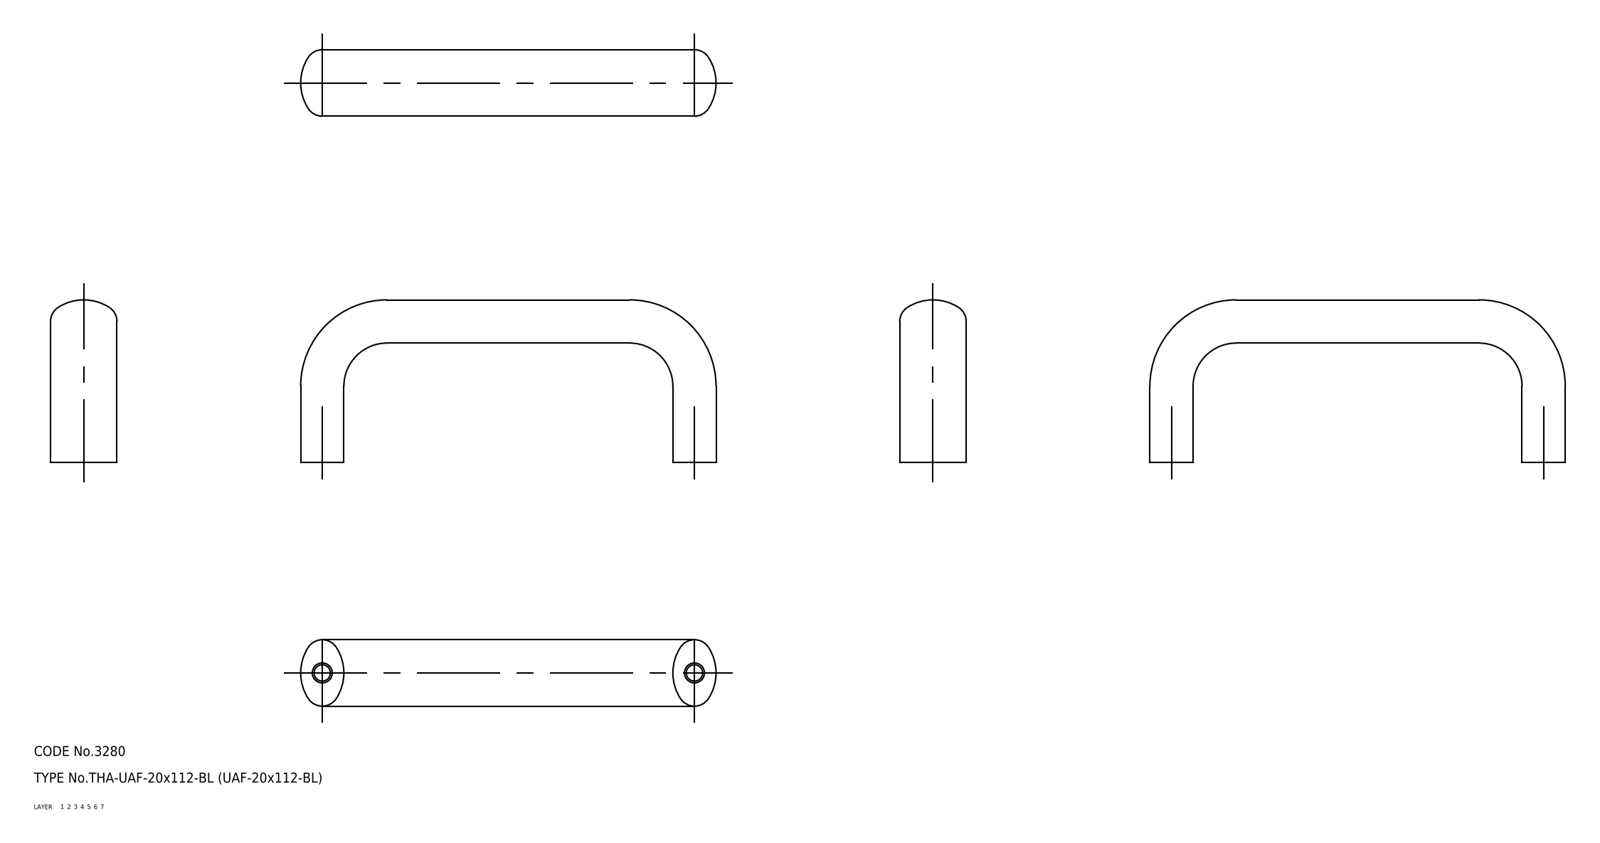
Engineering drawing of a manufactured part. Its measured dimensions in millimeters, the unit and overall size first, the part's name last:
Units: millimetres
Overall size (bounding box): 125 × 49.01 × 20
Volume: 36 198 mm³ · Surface area: 10 230 mm²
Bodies: 1 solid, 18 faces (0 planar, 0 cylindrical, 18 other)
Part name (STEP PRODUCT): pull
STEP written by: CADfix (AUTOMOTIVE_DESIGN)
